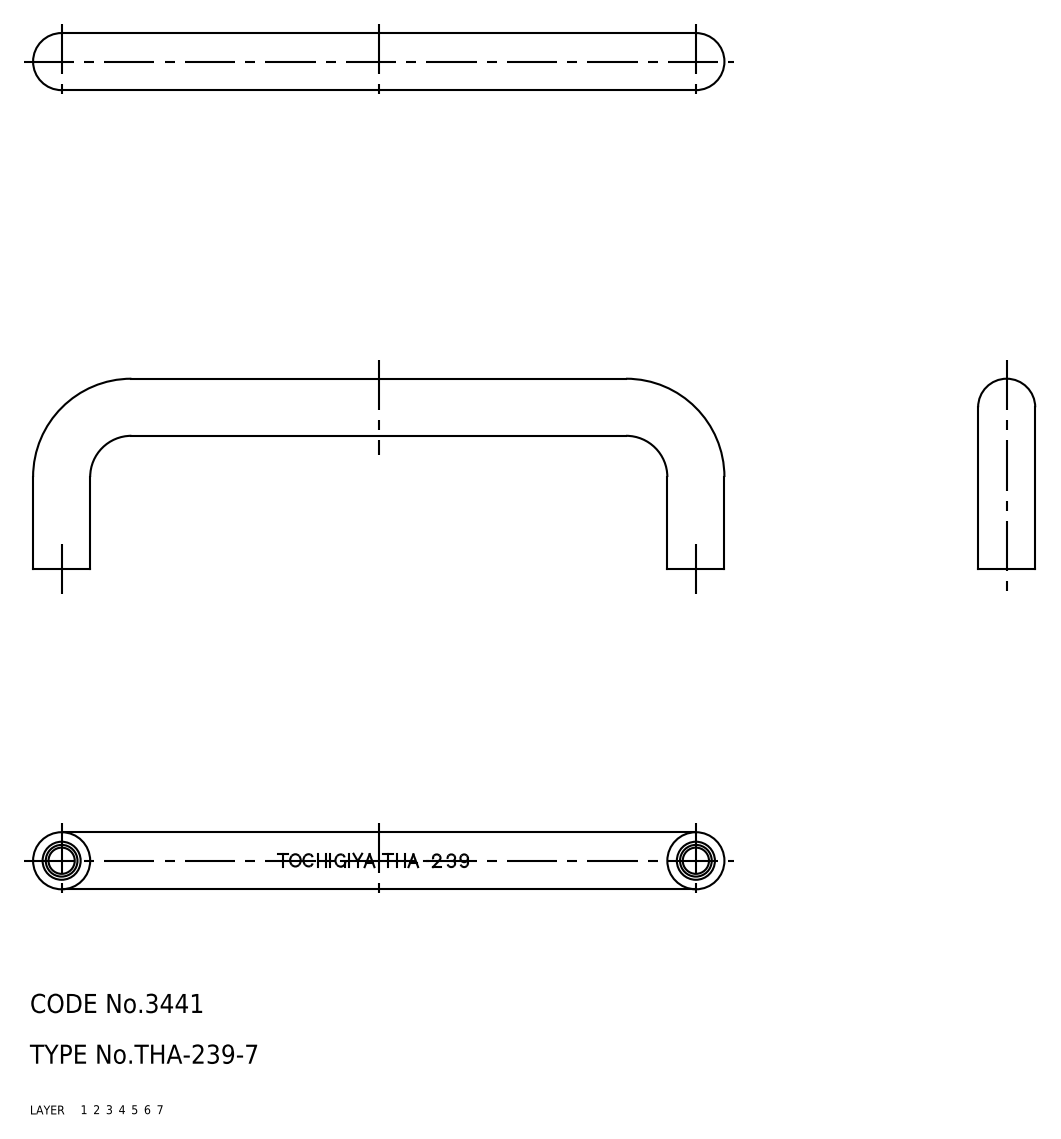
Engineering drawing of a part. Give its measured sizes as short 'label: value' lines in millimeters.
name: 67110193
written by: CADfix (AUTOMOTIVE_DESIGN)
unit: mm
bodies: 1 solid, 18 faces (0 planar, 0 cylindrical, 18 other)
size: 109 × 30 × 9
volume: 8 705 mm³; area: 4 386 mm²
